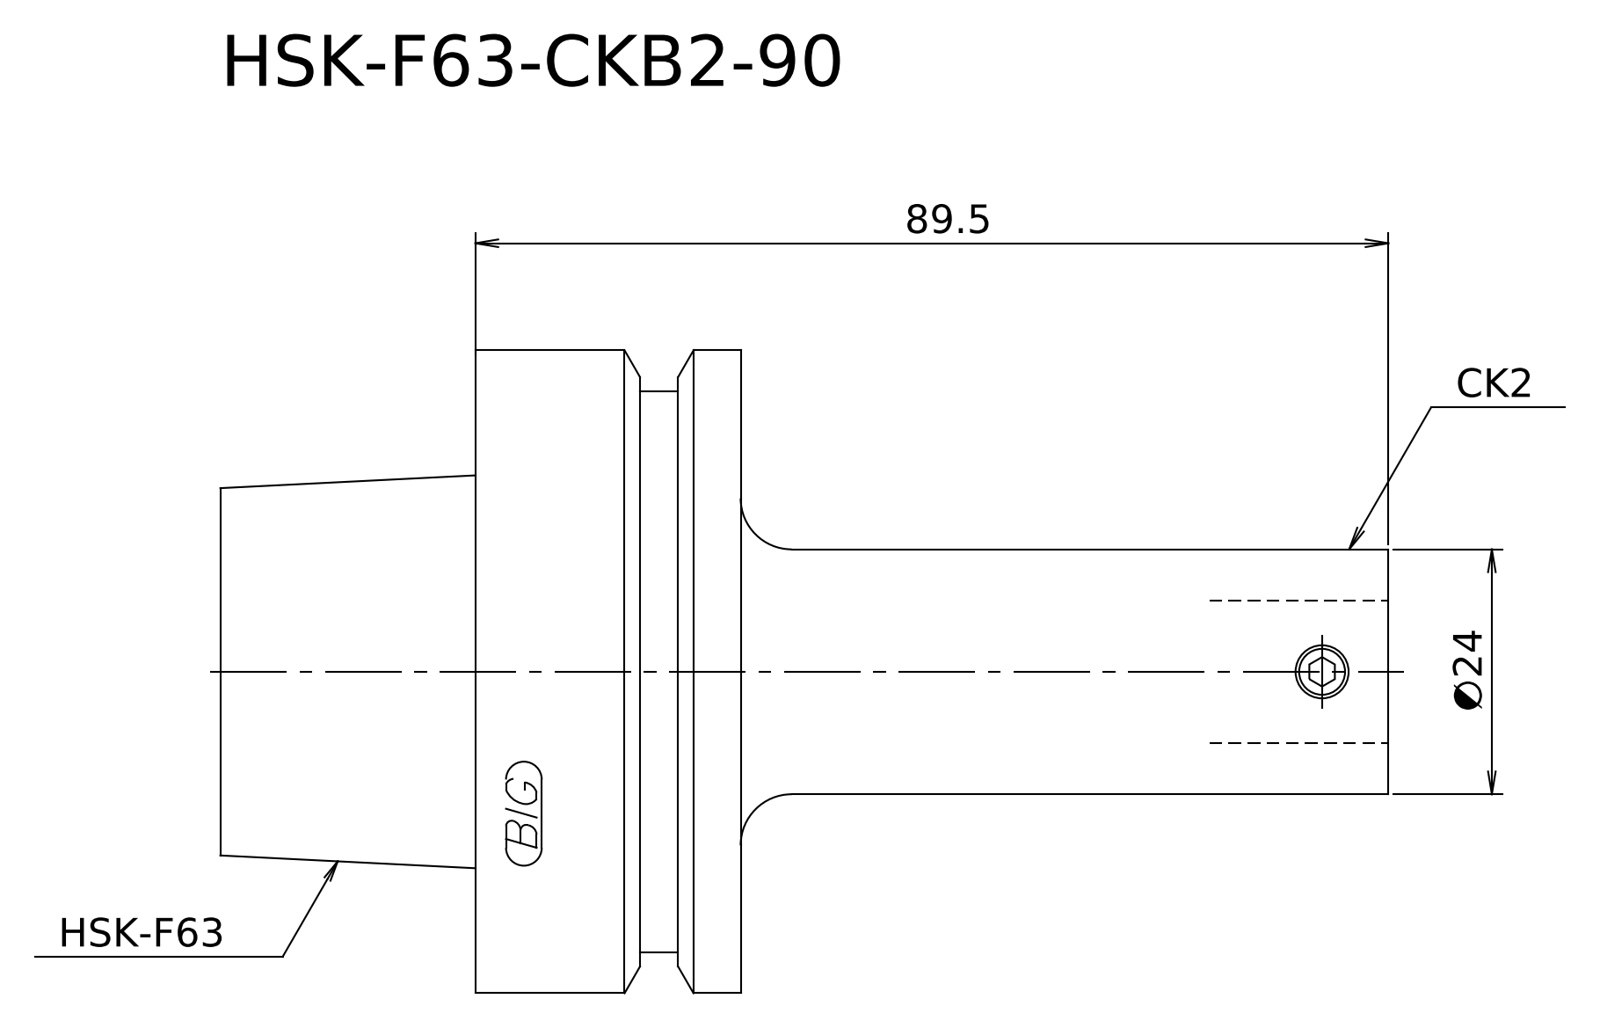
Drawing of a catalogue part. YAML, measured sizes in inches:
step_written_by: "Kubotek KeyCreator V8.5.1 (14335) (CONFIG_CONTROL_DESIGN)"
units: inches
bodies: {solids: 1, faces: 15, planar: 6, cylindrical: 5, other: 4}
overall_size: [4.508, 2.48, 2.48]
volume: 8.211
surface_area: 30.57
round_bosses_or_shafts:
  - {diameter: 2.48, count: 1}
  - {diameter: 2.165, count: 1}
  - {diameter: 1.508, count: 1}
  - {diameter: 0.945, count: 1}
face_to_face_distances: [1.024, 2.008, 0.984, 2.5, 3.524, 4.508, 2.741, 0.241, 0.783, 1.767]
